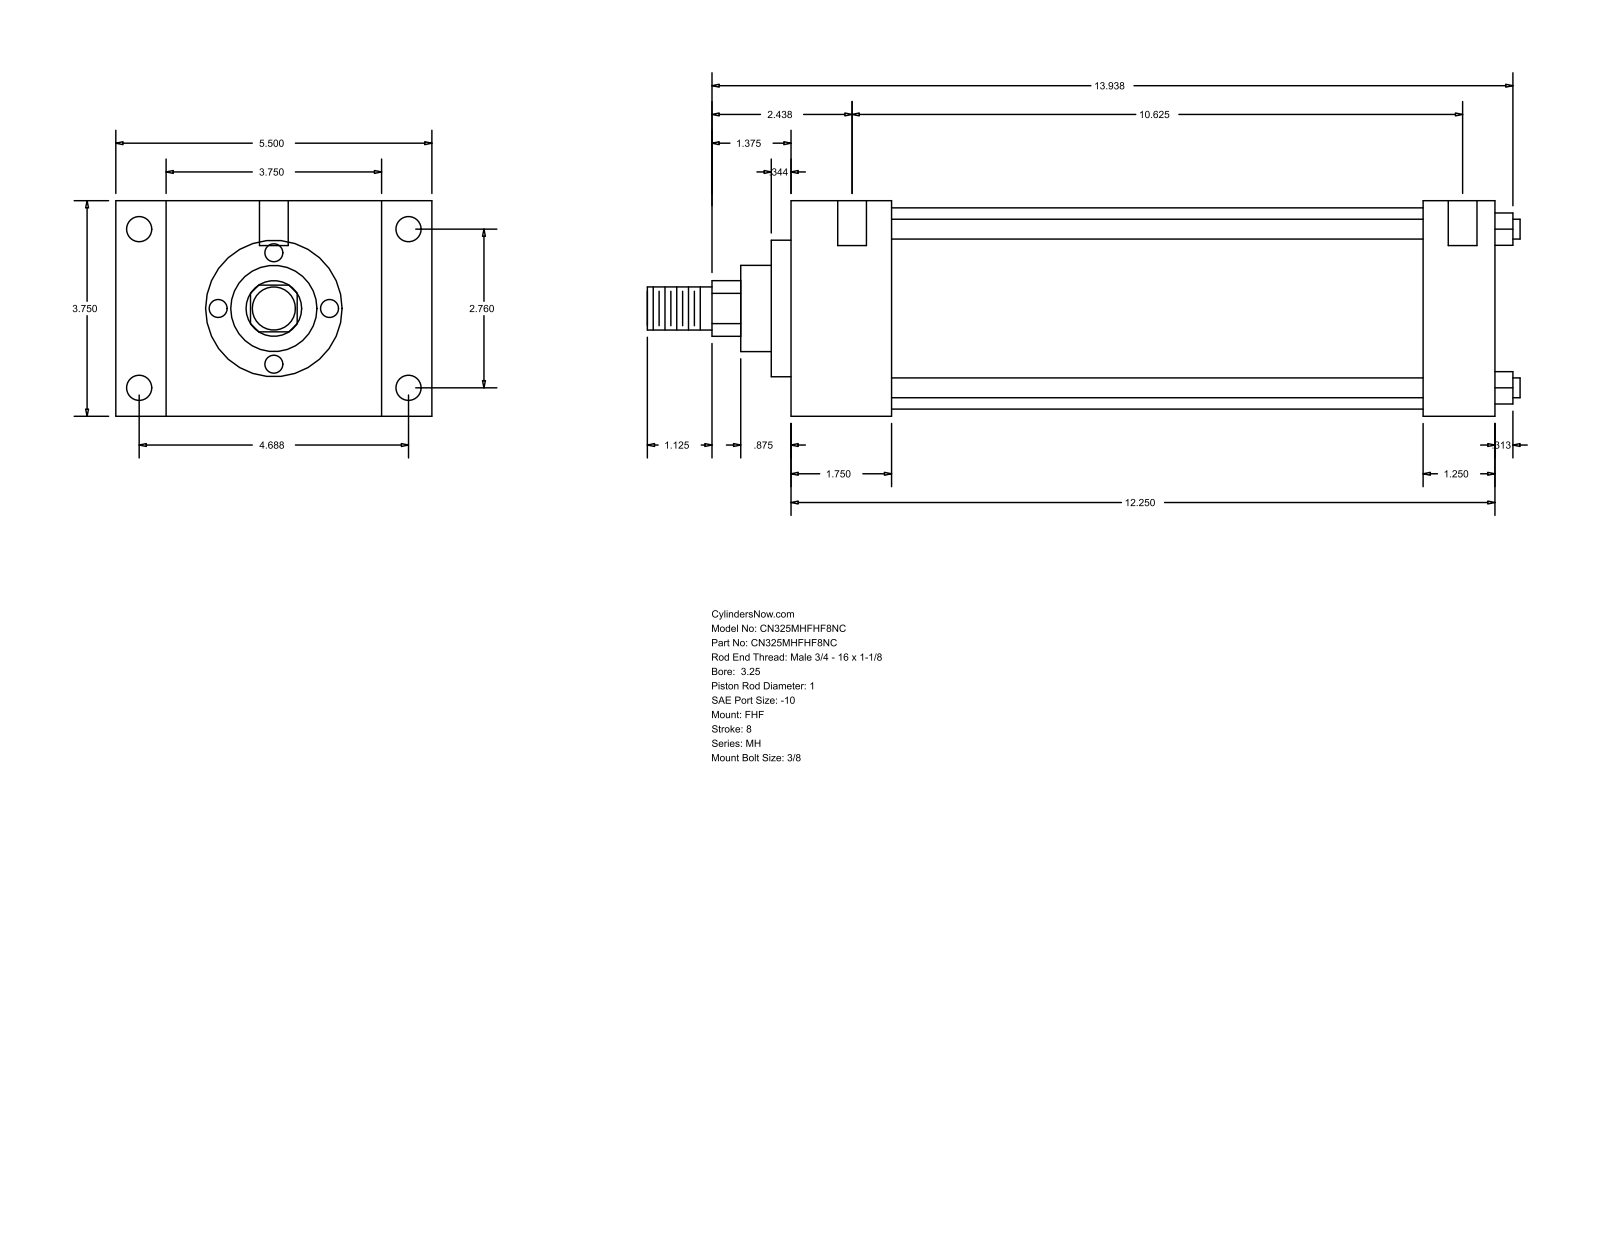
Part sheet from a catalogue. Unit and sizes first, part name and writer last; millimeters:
Units: millimetres
Overall size (bounding box): 385.76 × 139.7 × 95.25
Round holes (diameter × count): ⌀5.56 ×4, ⌀11.13 ×4, ⌀12.7 ×2
Round bosses / shafts (diameter × count): ⌀8.76 ×4, ⌀88.9 ×1, ⌀60.33 ×1, ⌀38.1 ×1, ⌀25.4 ×1, ⌀19.05 ×1
Partial cylindrical surfaces — rounded edges, fillets, slot ends (radius × count): R12.29 ×1
Main face-to-face distances: 95.24, 311.15, 44.46, 266.69, 22.23, 117.47, 139.7, 279.4, 234.94, 31.75
Hole centre spacings: 70.1, 119.06, 138.16, 276.22, 1.58, 4.76, 269.88, 271.46
Bodies: 0 solids, 90 faces (61 planar, 29 cylindrical, 0 other)
Part name (STEP PRODUCT): MH_FHF__0325_1
STEP written by: GSSL Pune (CONFIG_CONTROL_DESIGN)
